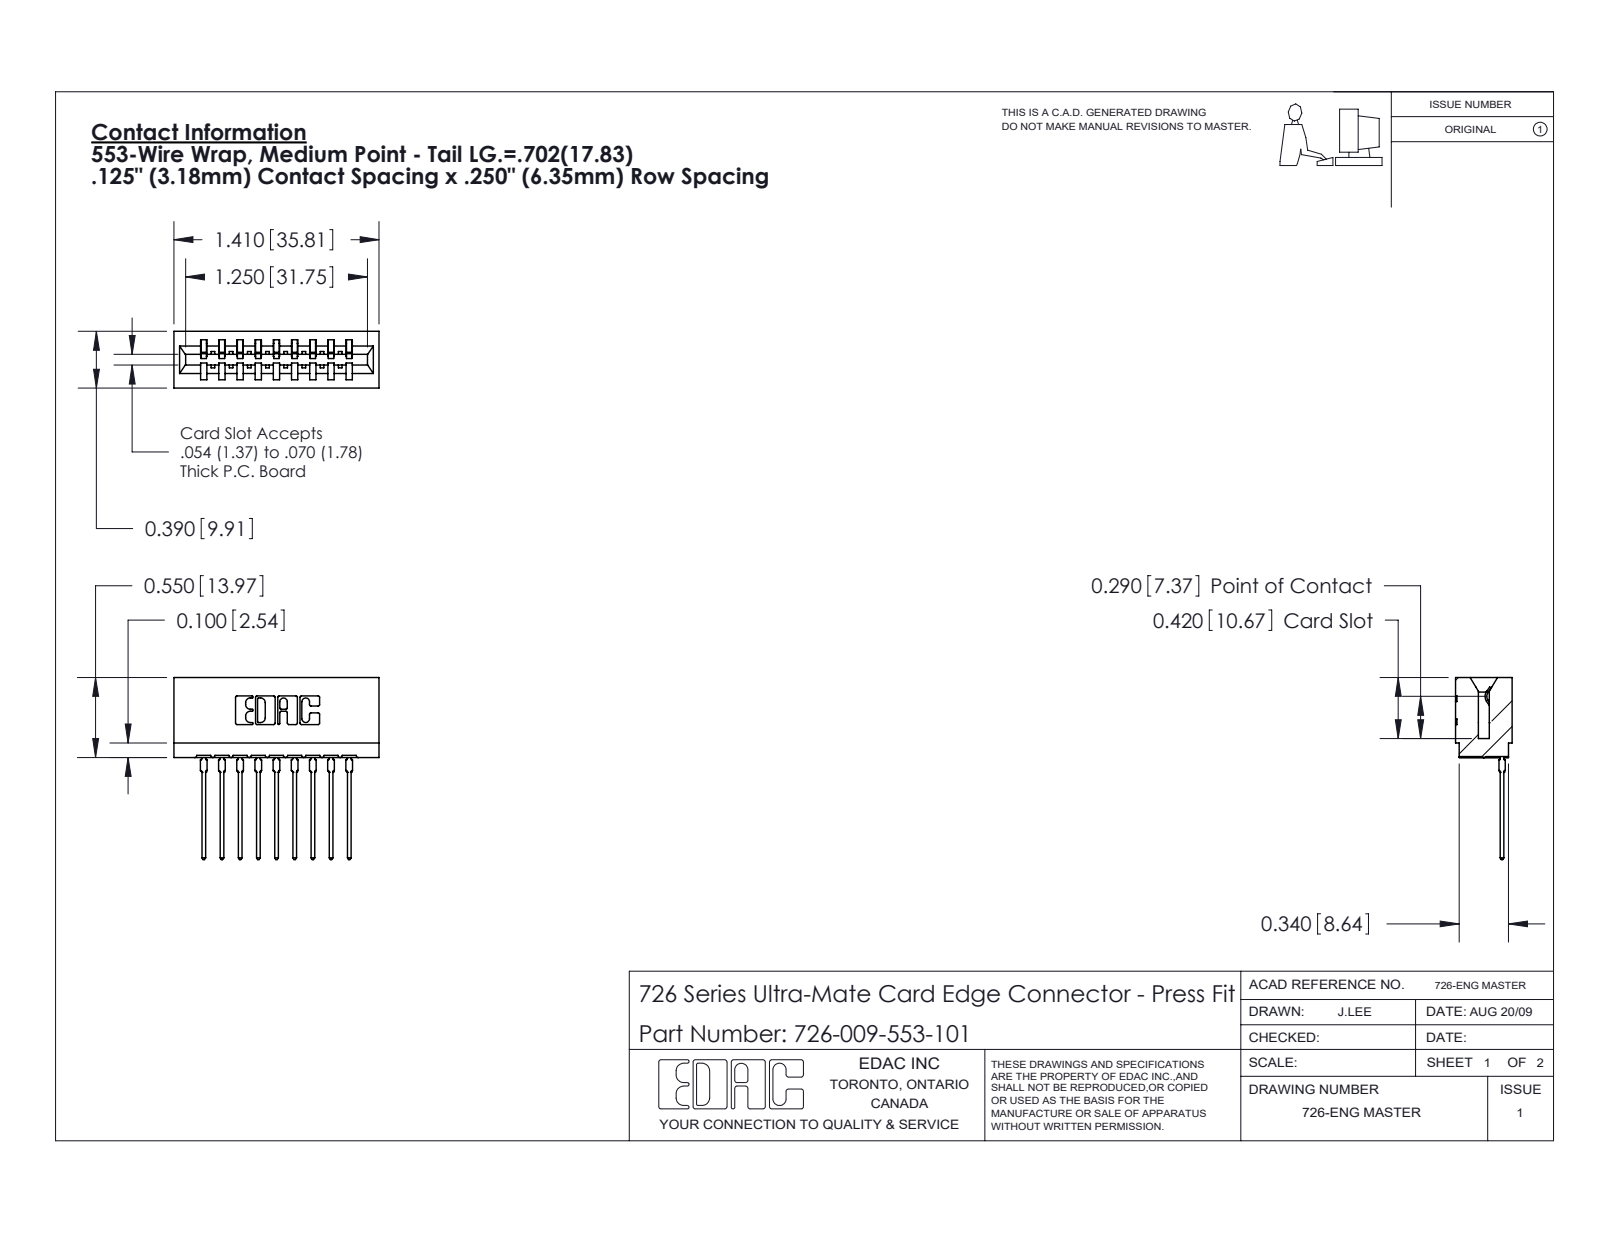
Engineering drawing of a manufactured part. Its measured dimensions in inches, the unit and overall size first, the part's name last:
Units: inches
Overall size (bounding box): 1.41 × 1.251 × 0.39
Partial cylindrical surfaces — rounded edges, fillets, slot ends (radius × count): R0.01 ×22, R0.021 ×18, R0.015 ×10, R0.007 ×6, R0.031 ×6, R0.005 ×4, R0.011 ×4, R0.026 ×3
Main face-to-face distances: 0.25, 0.5, 0.333, 0.042, 0.057, 0.125, 0.125, 0.208, 0.292, 0.083
Volume: 0.209 in³ · Surface area: 7.596 in²
Bodies: 10 solids, 1069 faces (622 planar, 213 cylindrical, 234 other)
Part name (STEP PRODUCT): 746-292-001_553; 726-009-553-101; 726 Part_.515 Slot Depth - 01
STEP written by: SolidWorks 2020 (CONFIG_CONTROL_DESIGN)
